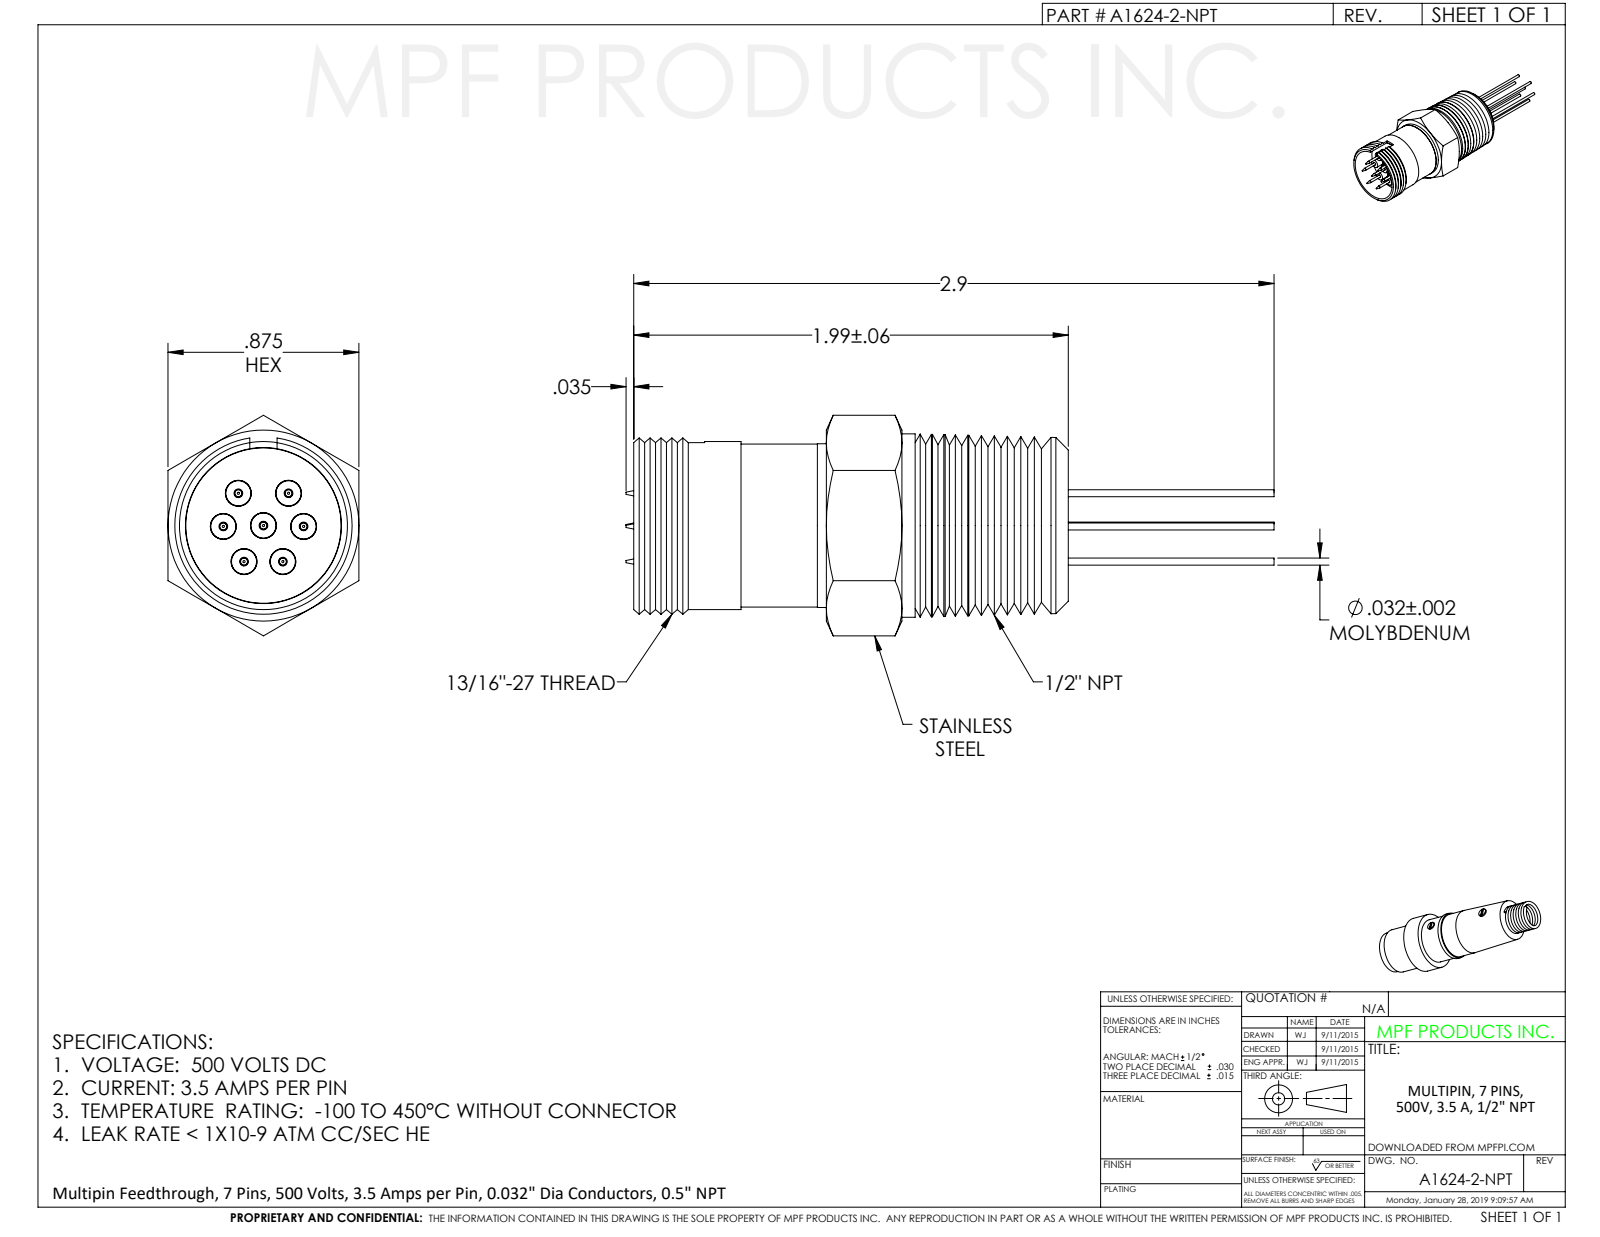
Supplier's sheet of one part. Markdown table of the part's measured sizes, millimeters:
| quantity | value |
| --- | --- |
| part name | A1624-2-QF |
| STEP written by | SolidWorks 2012 (CONFIG_CONTROL_DESIGN) |
| units | millimeters |
| bodies | 1 solid, 302 faces (61 planar, 90 cylindrical, 151 other) |
| overall size | 75.4 × 25.7 × 22.2 |
| volume | 6 690 mm³ |
| surface area | 9 884 mm² |
| round holes (diameter × count) | 15.9 × 1, 17.4 × 1, 18.2 × 1 |
| round bosses / shafts (diameter × count) | 3.6 × 7, 3.2 × 7, 0.8 × 7, 21.3 × 1, 19.6 × 1, 19.1 × 1, 19 × 1, 17 × 1 |
| partial cylindrical surfaces (radius × count) | 1.6 × 2, 9.2 × 1 |
| main face-to-face distances | 22.2, 1.6, 14.2, 12.6, 24.6, 23, 10.3, 2.5, 4.1, 16.8 |
